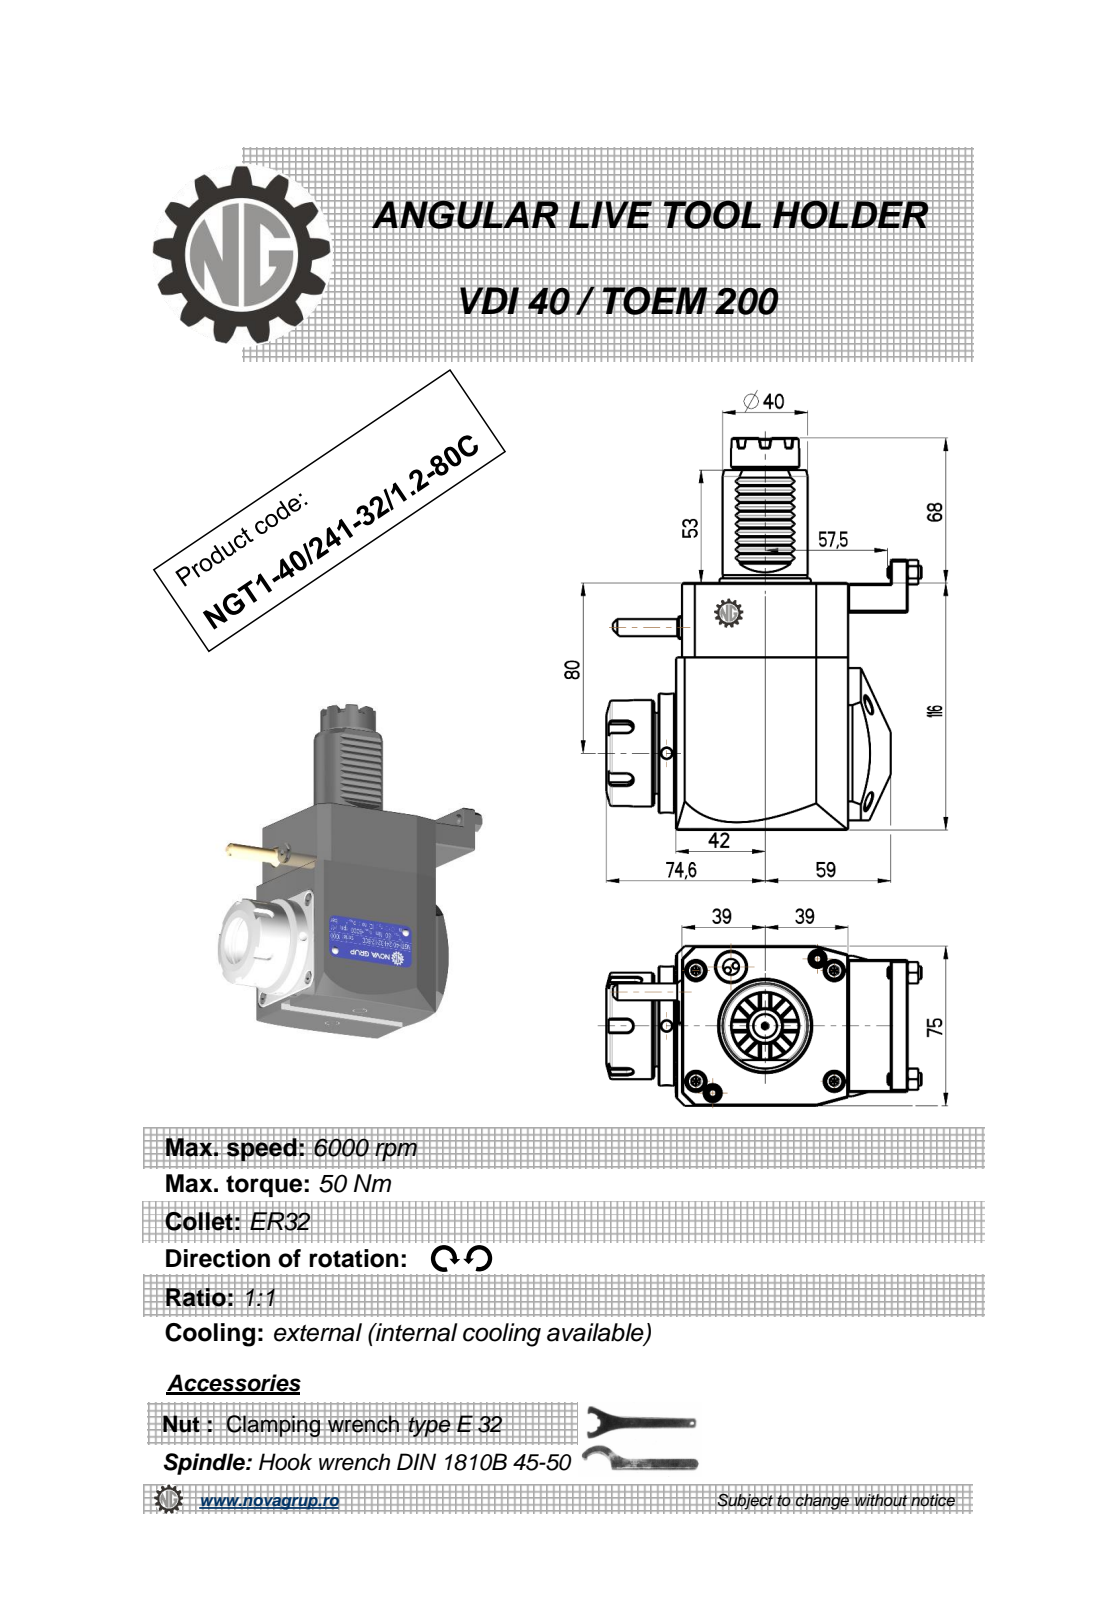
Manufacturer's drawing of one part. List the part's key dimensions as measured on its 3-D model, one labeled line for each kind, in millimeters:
Part name (STEP PRODUCT): NGT1_40_241_32_1_2_80C
STEP written by: PRO/ENGINEER BY PARAMETRIC TECHNOLOGY CORPORATION, 2010280 (CONFIG_CONTROL_DESIGN)
Units: millimetres
Bodies: 1 solid, 495 faces (217 planar, 89 cylindrical, 189 other)
Overall size (bounding box): 184 × 148.1 × 76.6
Volume: 902 531 mm³ · Surface area: 76 376 mm²
Round holes (diameter × count): ⌀5 ×3, ⌀3 ×1, ⌀27 ×1, ⌀42 ×1
Round bosses / shafts (diameter × count): ⌀6 ×2, ⌀56 ×1, ⌀50 ×1, ⌀41.4 ×1, ⌀41 ×1, ⌀40 ×1, ⌀32 ×1, ⌀16.8 ×1
Partial cylindrical surfaces — rounded edges, fillets, slot ends (radius × count): R0.3 ×10, R0.31 ×10, R0.22 ×6, R3 ×5, R0.5 ×1, R8.6 ×1, R40 ×1
Main face-to-face distances: 75, 116, 0.5, 109, 81, 3, 8, 78, 14, 11
Hole centre spacings: 61.13
